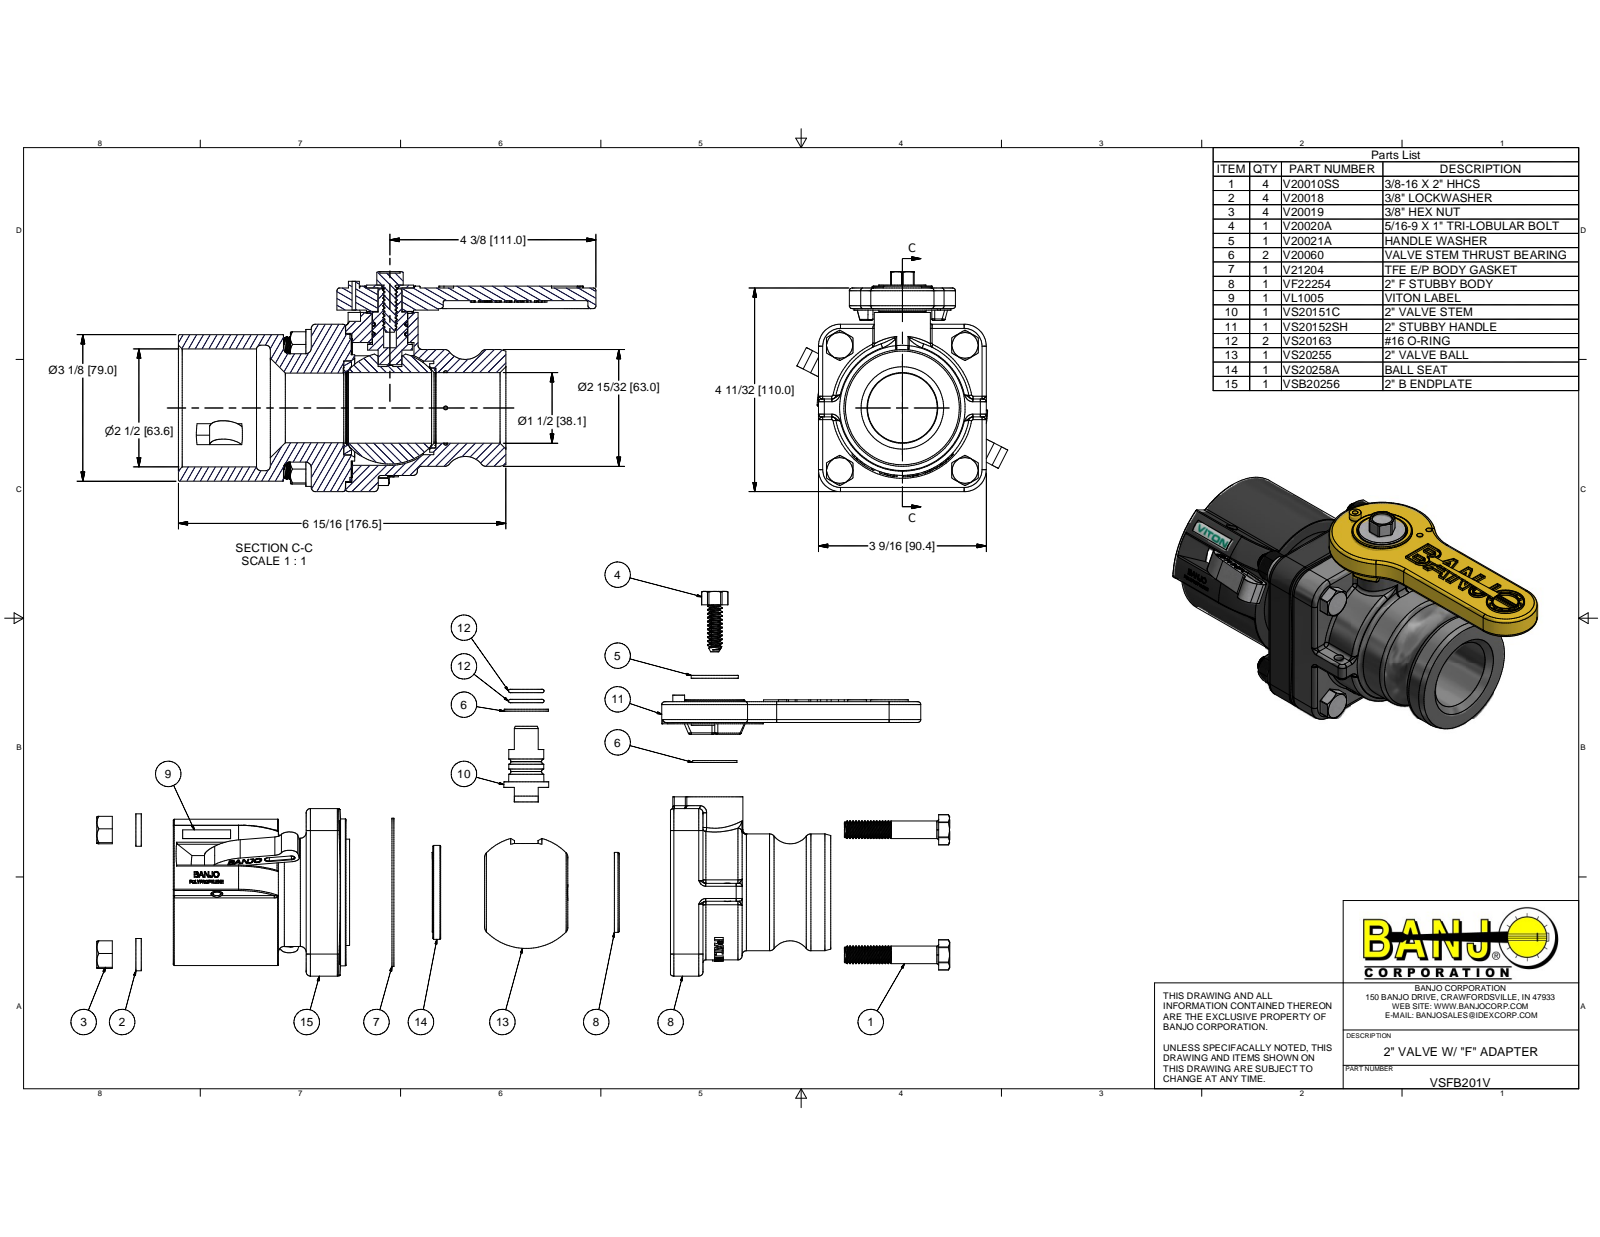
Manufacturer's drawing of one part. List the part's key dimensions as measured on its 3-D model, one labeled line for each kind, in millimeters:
Part name (STEP PRODUCT): VXF20254; VF22254Y; WS20258; VF22254 (+8 more)
STEP written by: Autodesk Inventor 2015 (AUTOMOTIVE_DESIGN)
Units: millimetres
Bodies: 31 solids, 3105 faces (1248 planar, 670 cylindrical, 1187 other)
Overall size (bounding box): 225.04 × 118.75 × 113.61
Volume: 608 957 mm³ · Surface area: 183 379 mm²
Round holes (diameter × count): ⌀10.31 ×8, ⌀7.81 ×4, ⌀9.52 ×4, ⌀9.78 ×4, ⌀2.03 ×2, ⌀3.3 ×2, ⌀5.08 ×2, ⌀6.35 ×2, ⌀6.55 ×2, ⌀3 ×1, ⌀6.81 ×1, ⌀9.02 ×1
Round bosses / shafts (diameter × count): ⌀8.24 ×60, ⌀17.46 ×4, ⌀9.52 ×4, ⌀6.6 ×2, ⌀6.32 ×2, ⌀80.01 ×1, ⌀79.3 ×1, ⌀63.04 ×1
Partial cylindrical surfaces — rounded edges, fillets, slot ends (radius × count): R1.52 ×24, R2.29 ×21, R0.76 ×17, R3.17 ×8, R4.12 ×8, R4.57 ×6, R1.91 ×4, R8.12 ×4
Main face-to-face distances: 12.7, 90.42, 2.92, 21.46, 18.54, 17.52, 6.86, 36.06, 14.6, 1.02
Hole centre spacings: 67.39, 47.56, 47.74, 67.26, 67.52, 95.3, 40.46, 46.12
